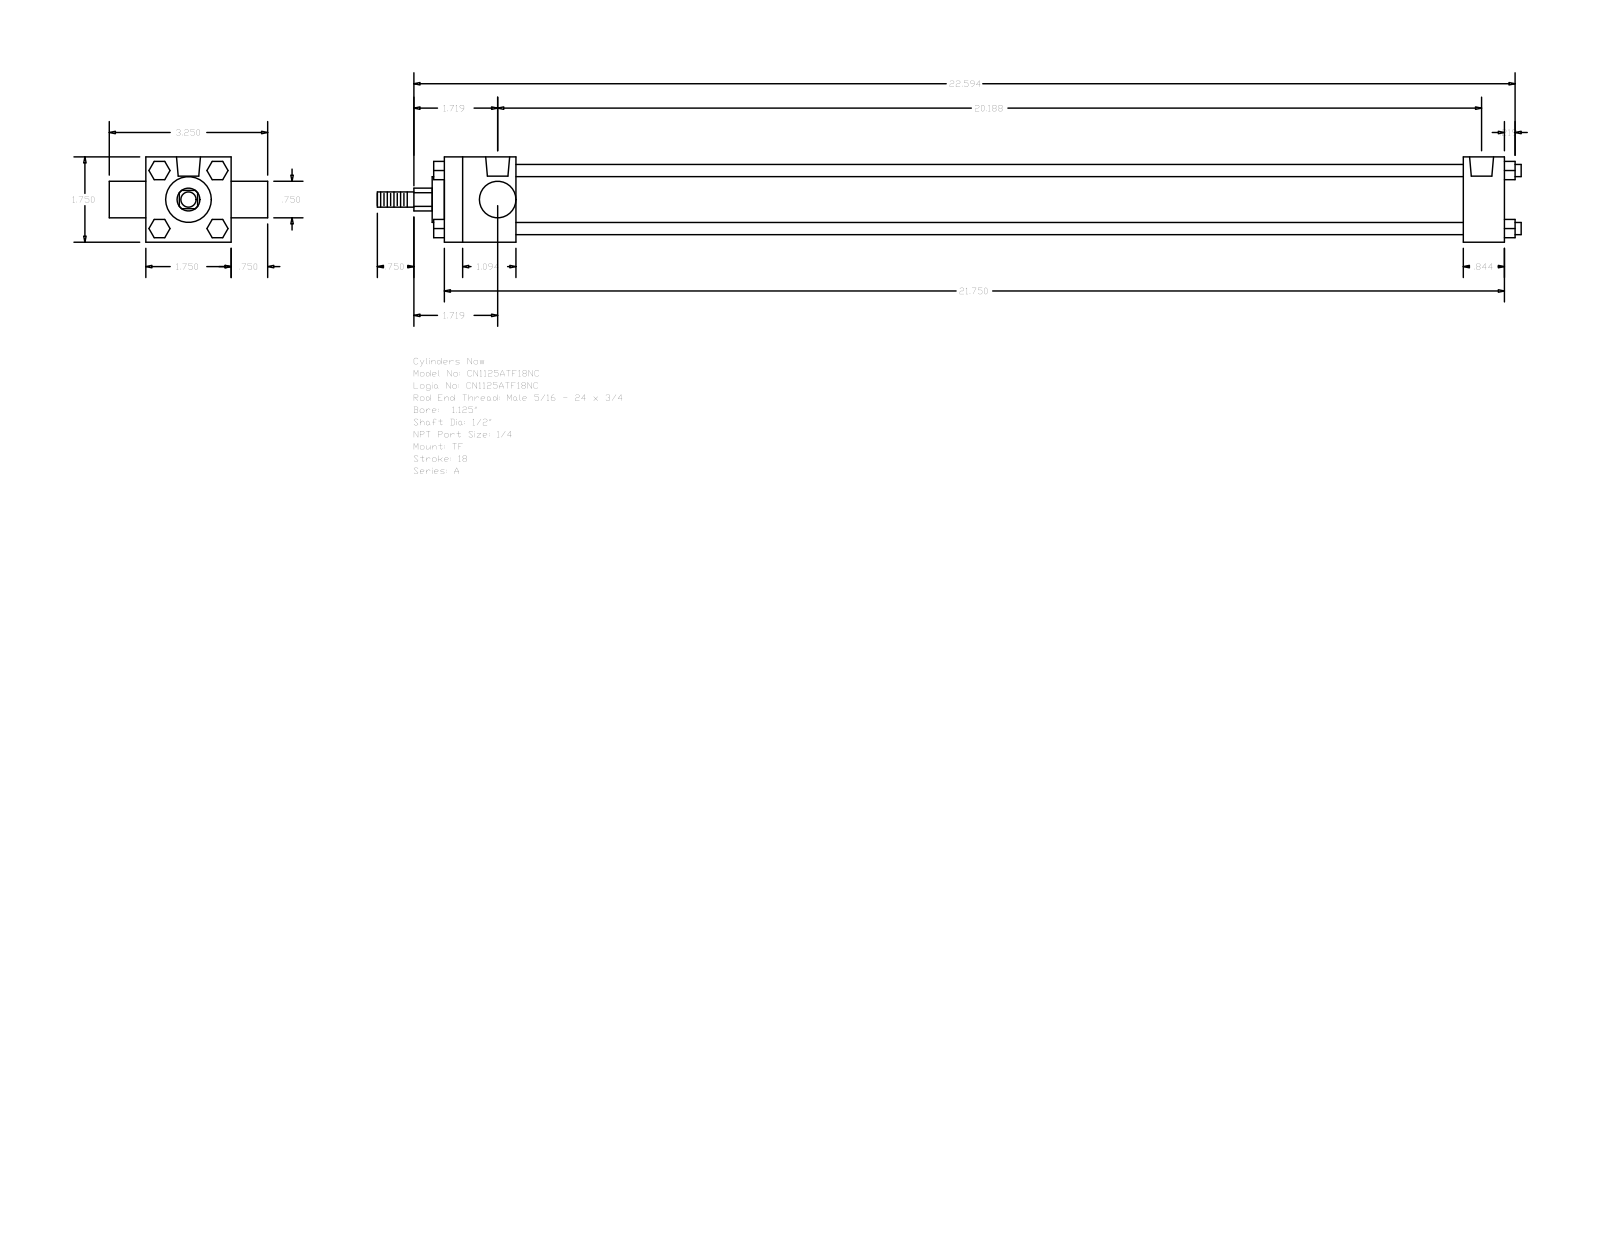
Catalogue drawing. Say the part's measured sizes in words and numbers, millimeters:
The part is named "A_TF__0112_0.5". Its 3-D file was written by "GSSL Pune (CONFIG_CONTROL_DESIGN)". It is 0 solids with 120 faces: 92 planar, 28 cylindrical and 0 other. Overall it measures 596.11 by 82.55 by 44.45 millimeters. Round holes: 3 of diameter 5.56, 2 of diameter 12.49. Round bosses or shafts: 4 of diameter 6.35, 1 of diameter 31.88, 1 of diameter 23.81, 1 of diameter 19.05, 1 of diameter 12.7, 1 of diameter 7.94. Partial cylindrical surfaces (rounded edges, fillets, slot ends): 1 of radius 5.94. The main face-to-face distances are 44.46, 552.45, 531.01, 21.44, 37.3, 493.71, 515.15, 19.04, 63.5, 9.53. The hole center spacings are 1.58, 1.59, 509.59, 511.17, 511.18, 512.76.
